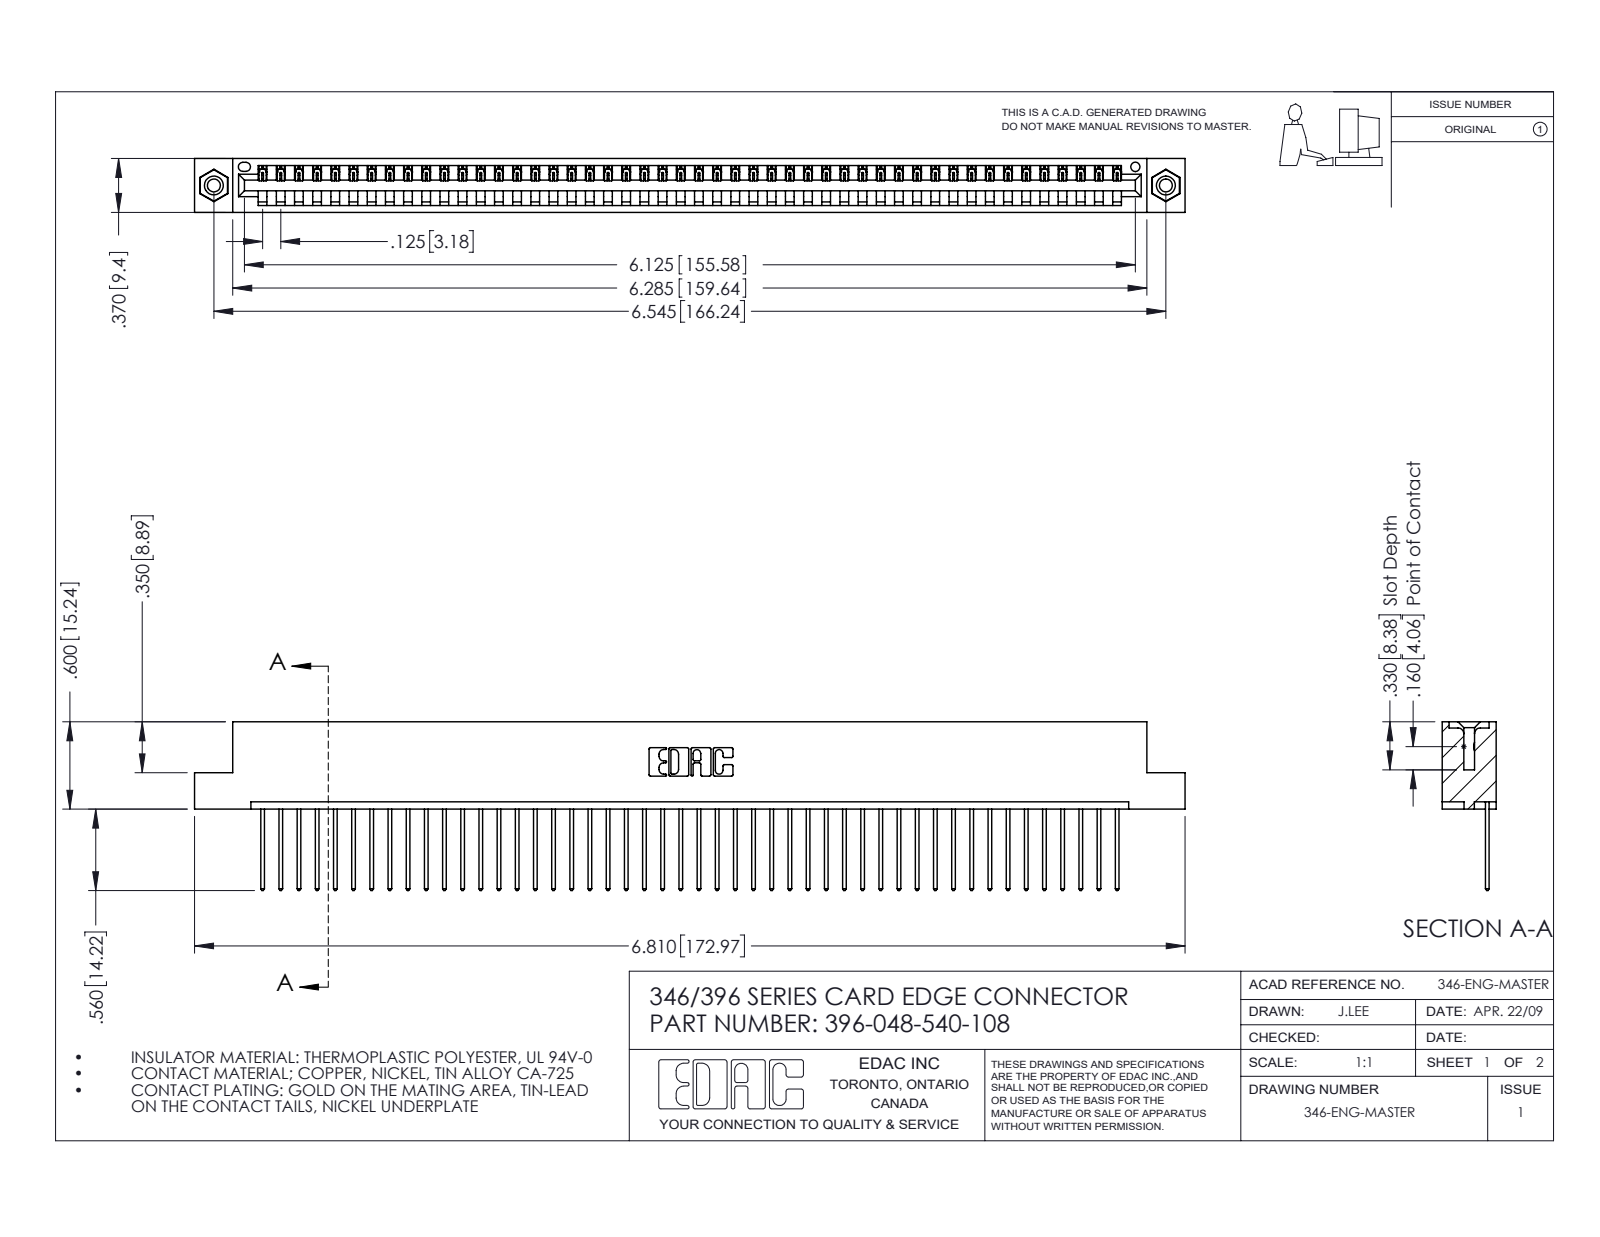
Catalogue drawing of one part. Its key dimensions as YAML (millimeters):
part_name: "345-292-001_345-293-140; 396-048-540-108; 345-250-001_345-250-003-102; 346 Part_Flush Mounting Lugs - 0.156 Dia-TI"
step_written_by: "SolidWorks 2016 (CONFIG_CONTROL_DESIGN)"
units: millimeters
bodies: {solids: 51, faces: 2966, planar: 2028, cylindrical: 922, other: 16}
overall_size: [173, 29.5, 9.4]
volume: 16650
surface_area: 21380
round_holes:
  - {diameter: 2.3, count: 2}
  - {diameter: 3.2, count: 2}
  - {diameter: 4, count: 2}
  - {diameter: 1.6, count: 1}
round_bosses_or_shafts:
  - {diameter: 3.9, count: 2}
partial_cylinders:
  - {radius: 0.2, count: 96}
  - {radius: 0.3, count: 96}
  - {radius: 0.3, count: 22}
  - {radius: 0.2, count: 6}
  - {radius: 0.8, count: 6}
  - {radius: 0.7, count: 3}
  - {radius: 0.8, count: 2}
  - {radius: 1, count: 2}
face_to_face_distances: [1.2, 8.2, 9.4, 6.4, 1.8, 7.6, 0.6, 3.8, 5.6, 2.5]
hole_center_spacings: [6.2, 160.9, 166.2]
